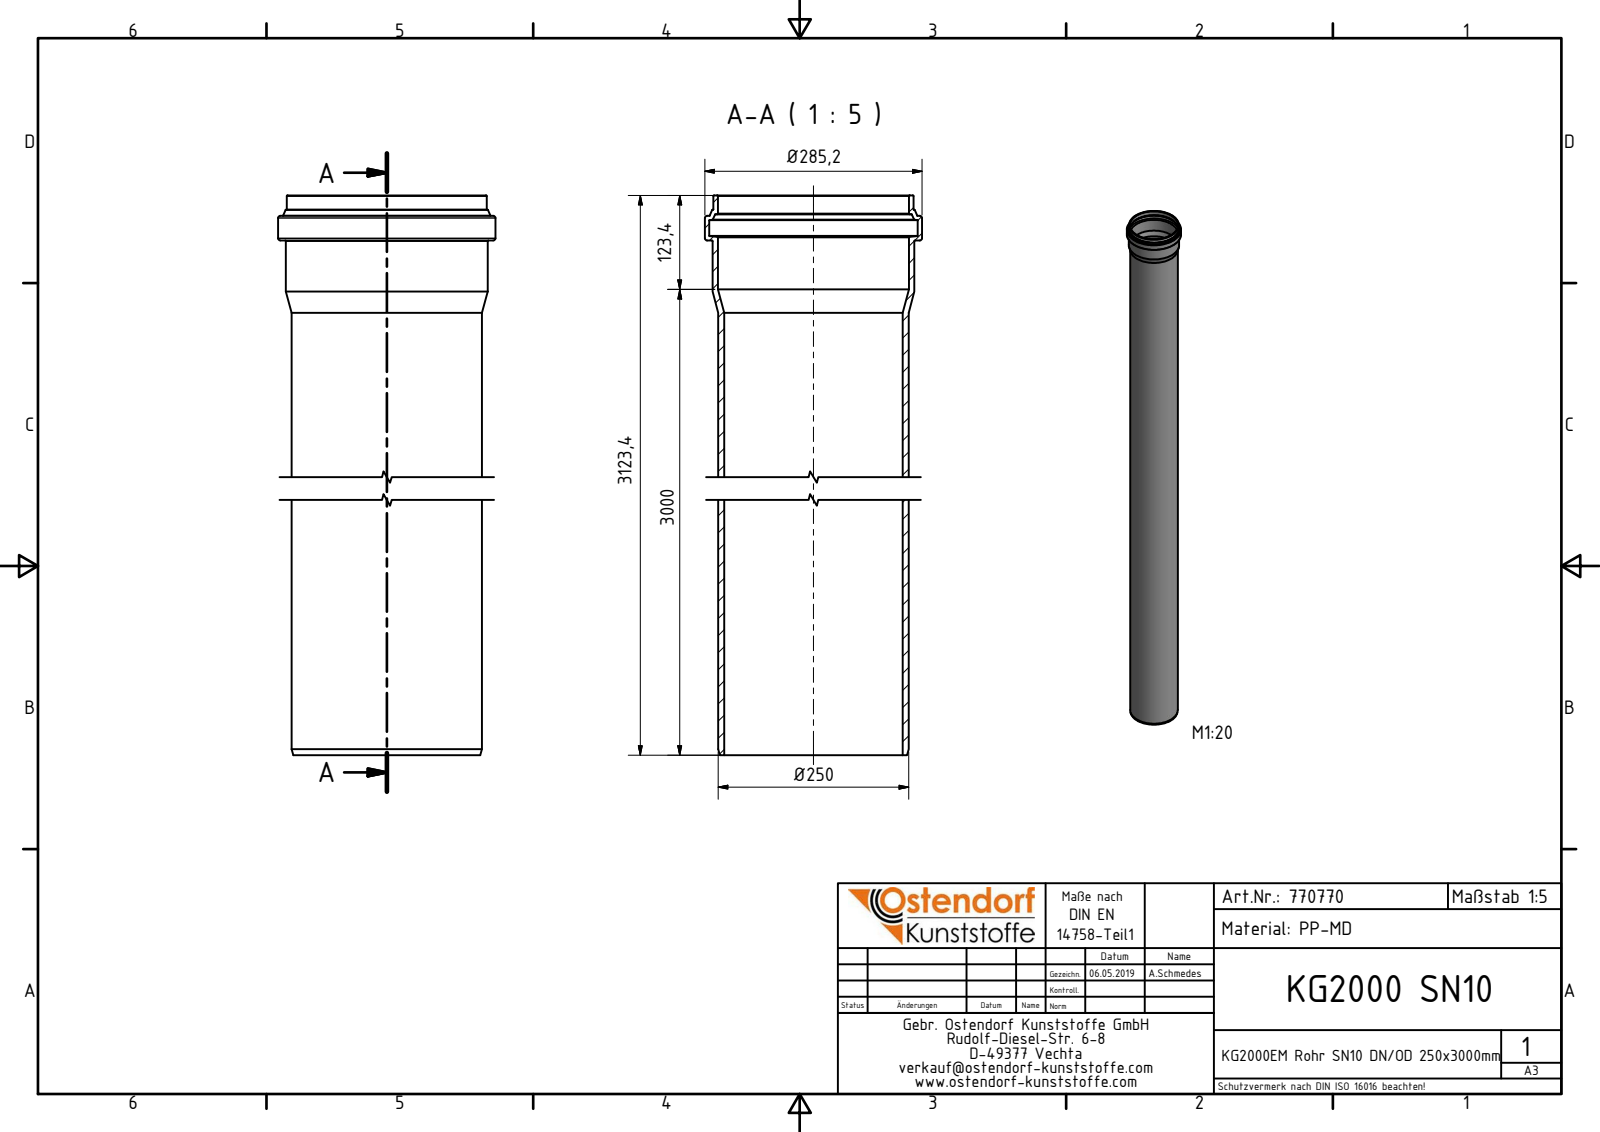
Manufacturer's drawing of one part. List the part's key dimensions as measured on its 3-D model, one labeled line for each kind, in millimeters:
Part name (STEP PRODUCT): 770770 KG2000EM Rohr SN10 DN-OD250x3000
STEP written by: Autodesk Inventor 2016 (AUTOMOTIVE_DESIGN)
Units: millimetres
Bodies: 1 solid, 35 faces (5 planar, 8 cylindrical, 22 other)
Overall size (bounding box): 3123.4 × 285.2 × 285.2
Volume: 18 320 000 mm³ · Surface area: 4 810 000 mm²
Round holes (diameter × count): ⌀234.6 ×1, ⌀251 ×1, ⌀273.6 ×1
Round bosses / shafts (diameter × count): ⌀285.2 ×1, ⌀265 ×1, ⌀262.6 ×1, ⌀250 ×1
Main face-to-face distances: 3064.2, 3123.4, 59.2, 3096.7, 32.5, 26.7, 3104.53, 40.33, 7.83, 18.87
